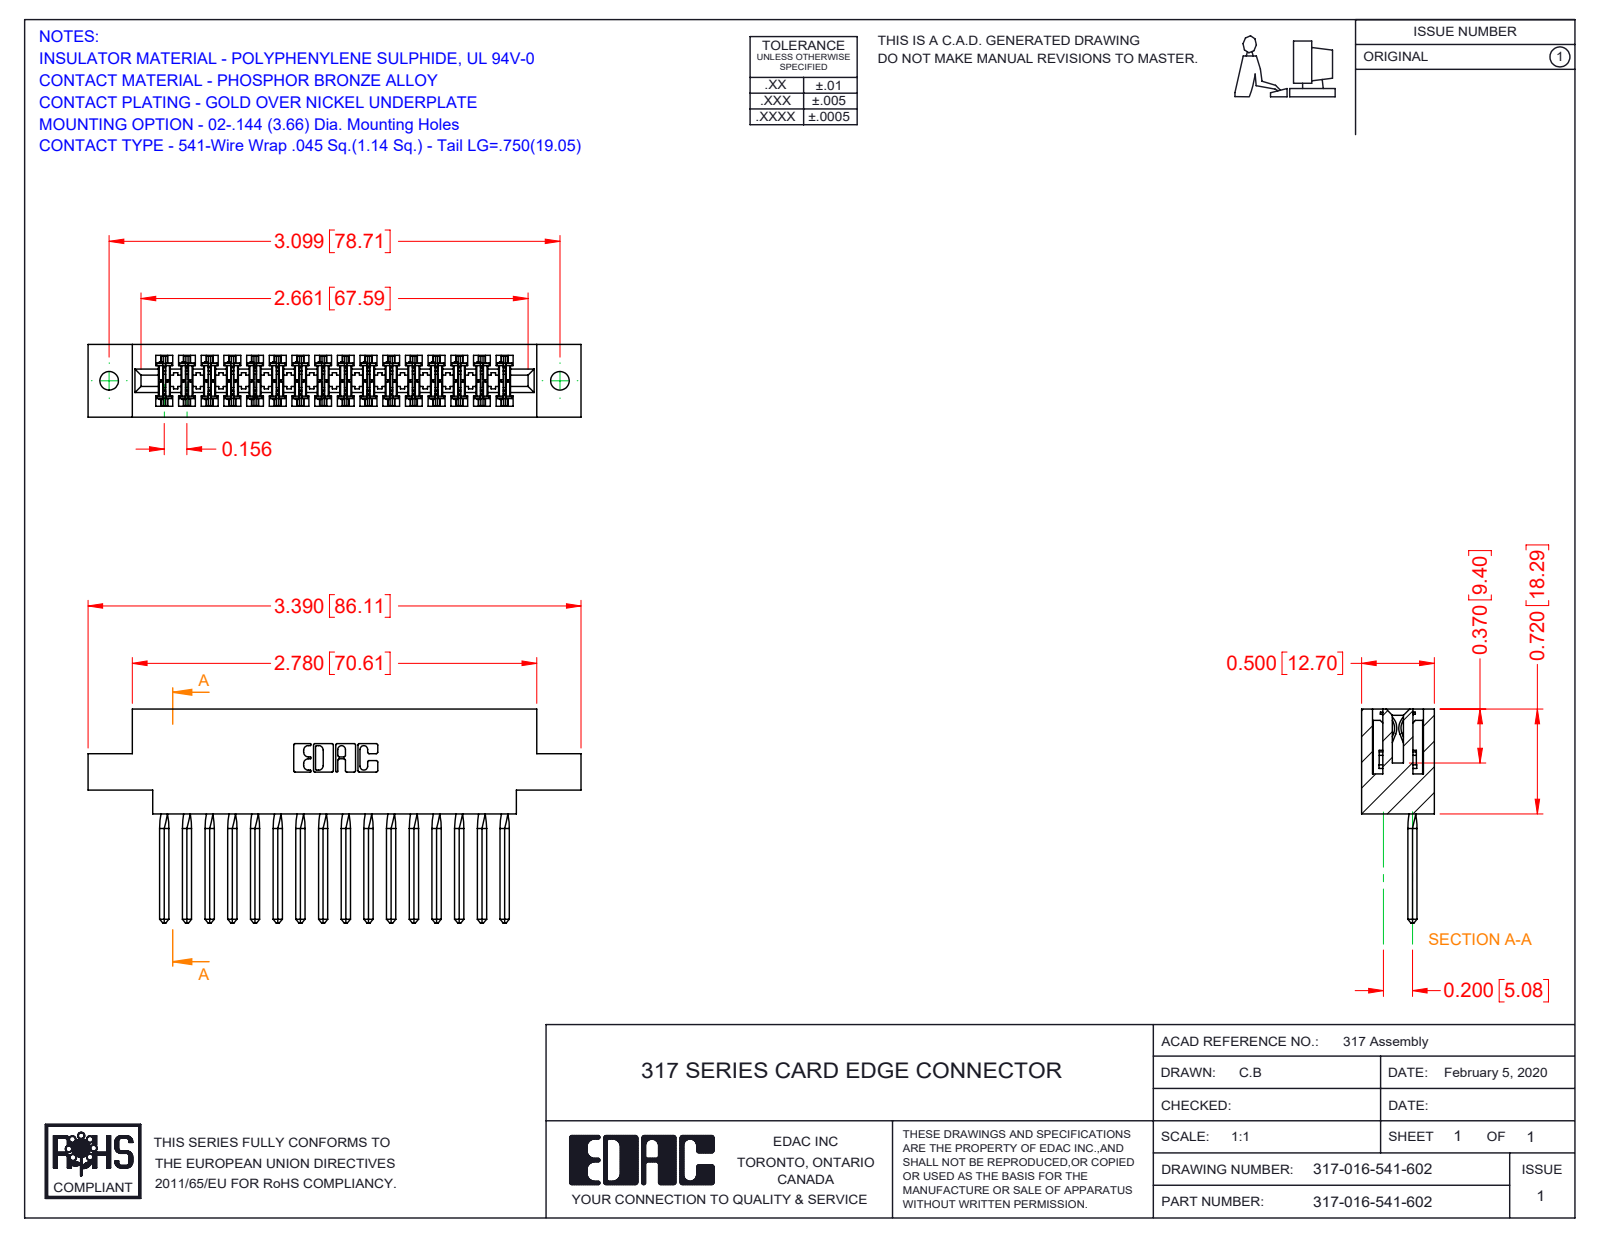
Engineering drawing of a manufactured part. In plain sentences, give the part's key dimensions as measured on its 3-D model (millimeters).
The part is named "317 Part_.144 Dia; 317-016-541-602; 317-290-002_541". Its 3-D file was written by "SolidWorks 2016 (CONFIG_CONTROL_DESIGN)". It is 17 solids with 2534 faces: 2042 planar, 428 cylindrical and 64 other. Overall it measures 86.1 by 37.3 by 12.7 millimeters. Its volume is 13 100 cubic millimeters and its surface area 17 420 square millimeters. Round holes: 2 of diameter 3.3. Partial cylindrical surfaces (rounded edges, fillets, slot ends): 32 of radius 0.4, 22 of radius 0.3, 6 of radius 0.2, 6 of radius 0.8, 3 of radius 0.7, 2 of radius 2.4, 2 of radius 2.5, 2 of radius 2.8. The main face-to-face distances are 12.7, 1.9, 10.8, 2.8, 8.9, 5.6, 5, 1.7, 18.3, 19.6. The hole center spacings are 78.7.
